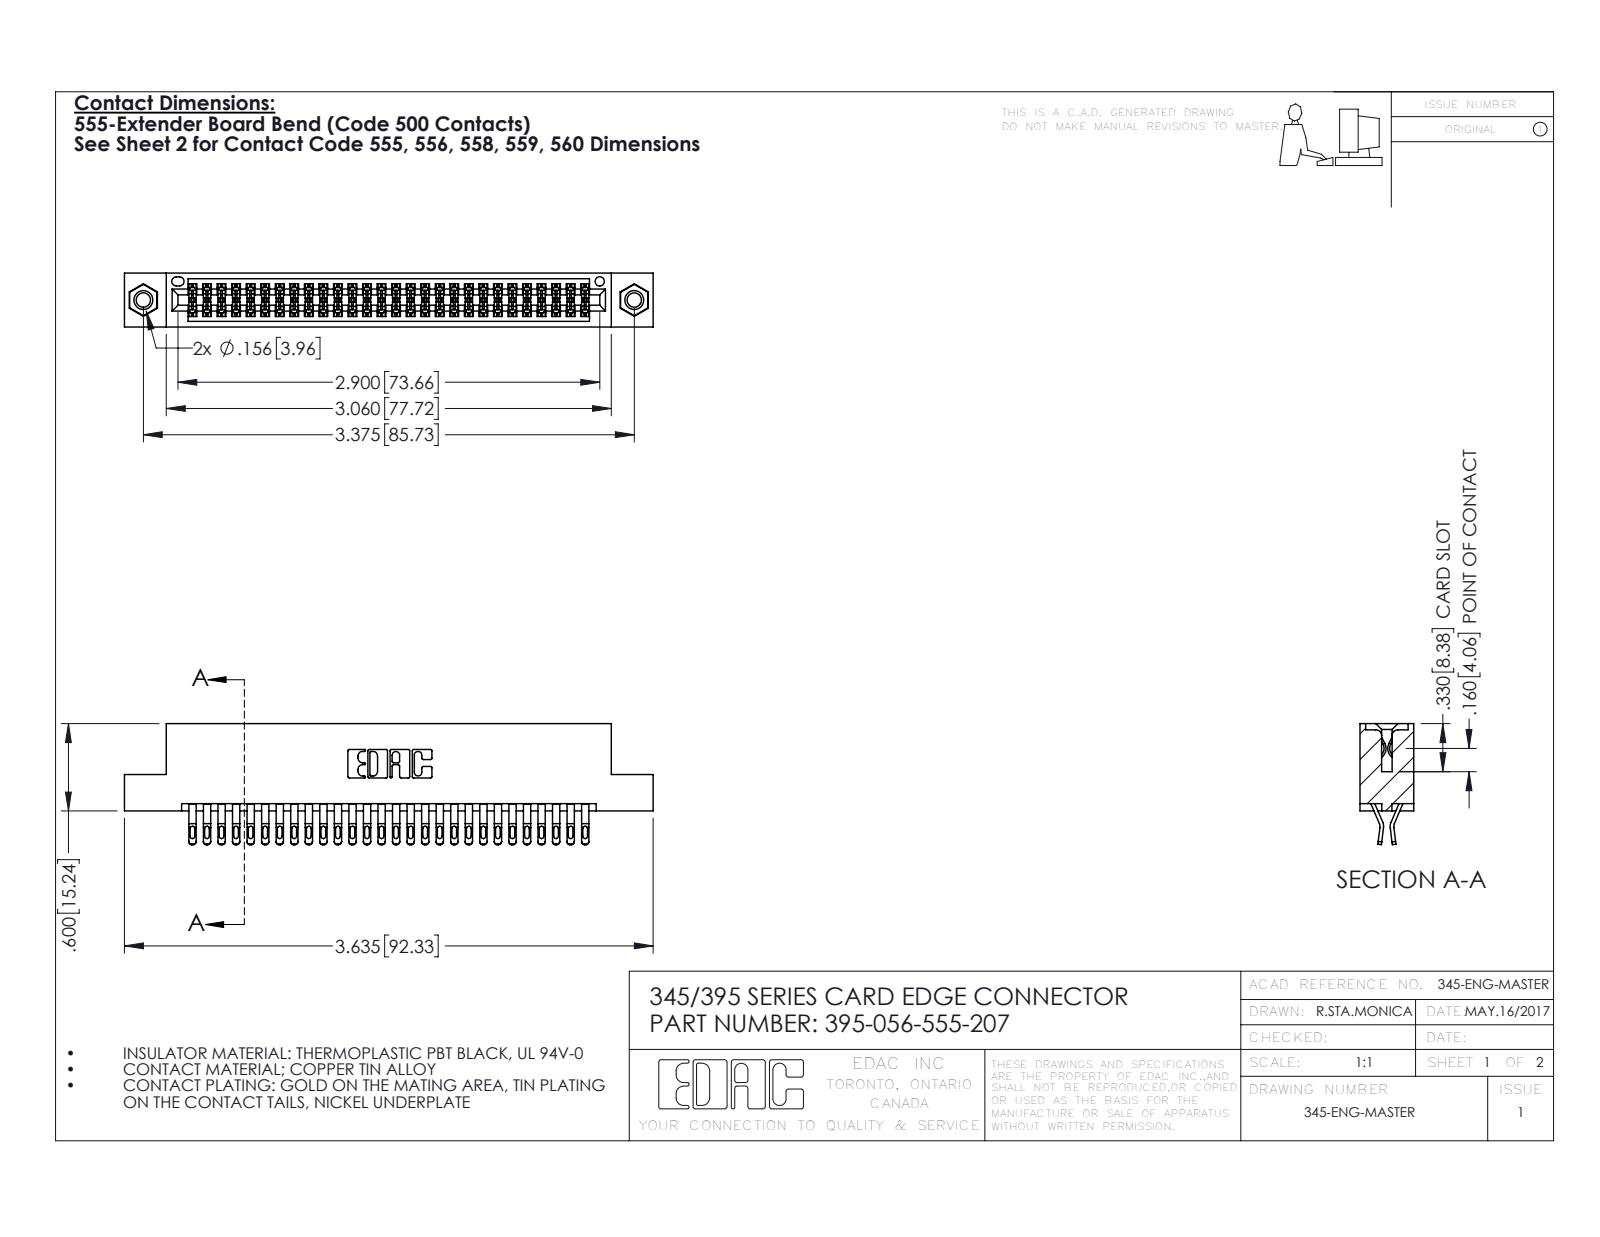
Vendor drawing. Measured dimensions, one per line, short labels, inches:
name: 345-250-001_345-250-005-103; 395-056-555-207; 345-292-001_555 Tail; 345 Part_Flush Mounting Lugs - 0.156 Dia-TI
written by: SolidWorks 2016 (CONFIG_CONTROL_DESIGN)
unit: in
bodies: 59 solids, 3322 faces (1848 planar, 1458 cylindrical, 16 other)
size: 3.635 × 0.832 × 0.37
volume: 0.548 in³; area: 21.09 in²
holes: 2× ⌀0.098, 2× ⌀0.125, 2× ⌀0.156, 1× ⌀0.064
bosses: 2× ⌀0.155
rounds: 140× R0.016, 112× R0.02, 84× R0.006, 22× R0.01, 6× R0.007, 6× R0.031, 3× R0.026, 2× R0.01
face distances: 0.072, 0.298, 0.2, 0.37, 0.025, 0.098, 0.272, 0.225, 0.175, 0.149
hole spacings: 0.27, 3.14, 3.375
